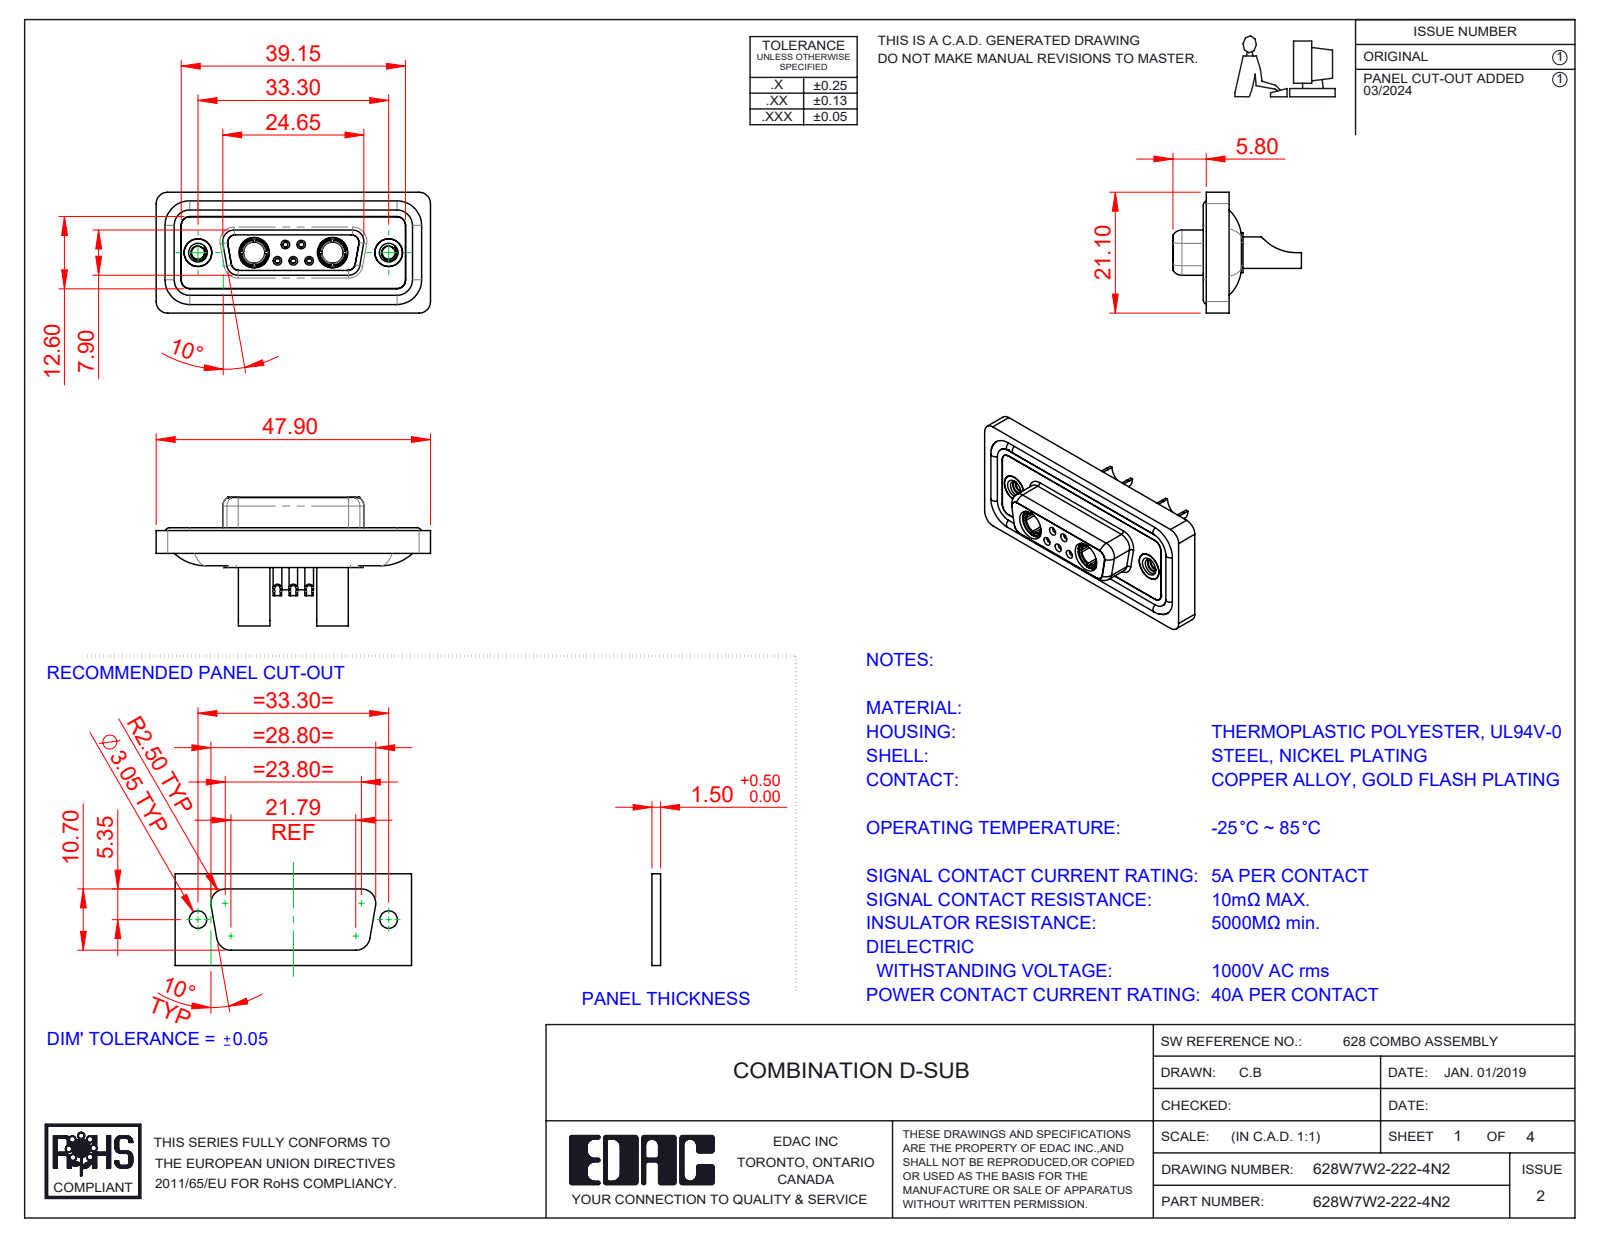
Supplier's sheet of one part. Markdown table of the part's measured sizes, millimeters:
| quantity | value |
| --- | --- |
| part name | 628Combo Contact Row 2_22; 628Combo Housing_7W2; 628Combo Threaded Rivet_2; 628Combo Waterproof Housing_15 Contacts (+5 more) |
| STEP written by | SolidWorks 2023 (CONFIG_CONTROL_DESIGN) |
| units | millimeters |
| bodies | 16 solids, 815 faces (252 planar, 341 cylindrical, 222 other) |
| overall size | 47.9 × 22.45 × 21.1 |
| volume | 6 168 mm³ |
| surface area | 10 220 mm² |
| round holes (diameter × count) | 0.9 × 5, 1 × 5, 1.1 × 5, 1.5 × 5, 2 × 5, 4.85 × 4, 1.6 × 3, 1.7 × 2, 2.26 × 2, 3.7 × 2, 4 × 2, 4.05 × 2 |
| round bosses / shafts (diameter × count) | 1.6 × 6, 2.2 × 5, 5.5 × 2, 5.2 × 2, 4.96 × 2, 4.95 × 2, 4.8 × 2, 4.75 × 2 |
| partial cylindrical surfaces (radius × count) | 1.5 × 22, 2 × 20, 1.35 × 12, 1.6 × 8, 1 × 6, 0.25 × 4, 0.5 × 4, 0.6 × 4 |
| main face-to-face distances | 0.4, 1.6, 1.8, 0.5, 2.9, 1.1, 7.45, 5.65, 6.6, 7.05 |
| hole center spacings | 3.16, 2.77, 9.8, 23.5, 4.31, 4.33, 5.03, 5.04 |
